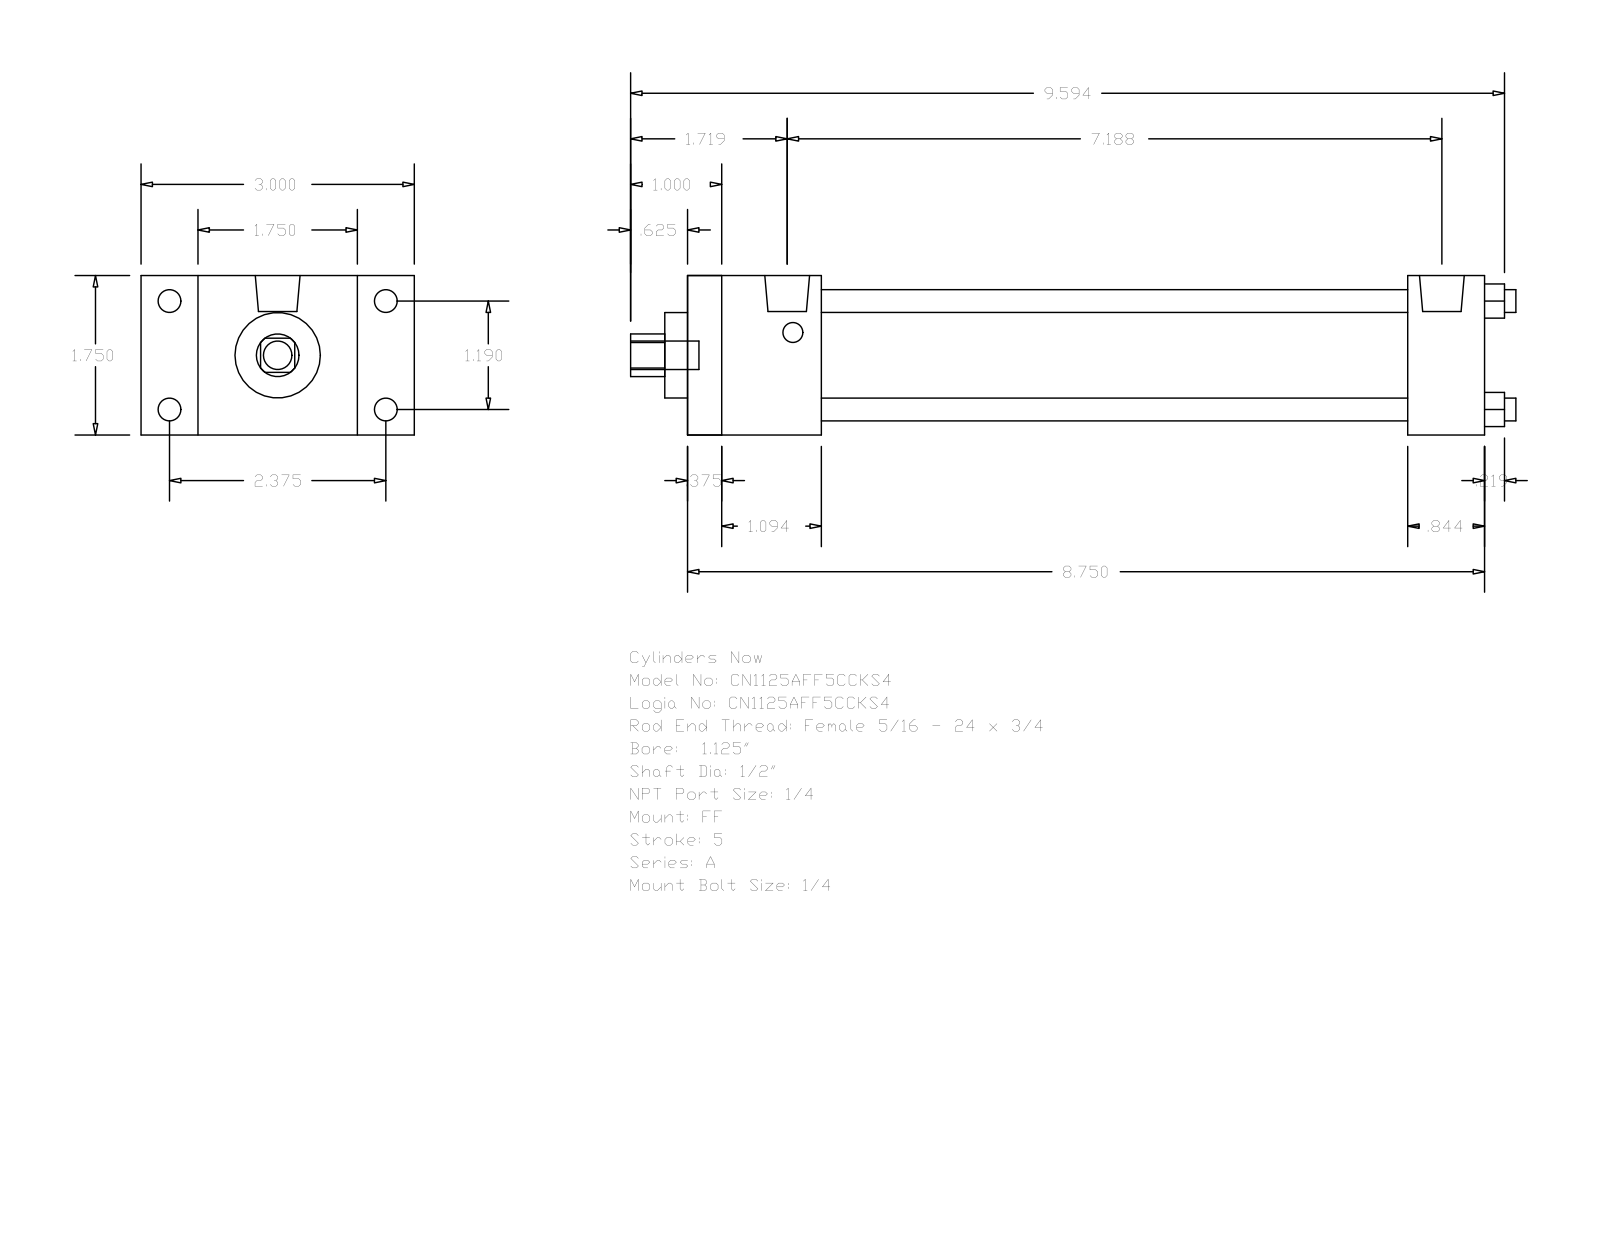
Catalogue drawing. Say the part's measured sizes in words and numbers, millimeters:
The part is named "A_FF__0112_0.5". Its 3-D file was written by "GSSL Pune (CONFIG_CONTROL_DESIGN)". It is 0 solids with 92 faces: 64 planar, 28 cylindrical and 0 other. Overall it measures 246.86 by 76.2 by 44.45 millimeters. Round holes: 4 of diameter 6.35, 1 of diameter 12.7, 1 of diameter 23.81, 1 of diameter 31.88. Round bosses or shafts: 4 of diameter 6.35, 4 of diameter 5.56, 2 of diameter 12.49, 1 of diameter 7.94. Partial cylindrical surfaces (rounded edges, fillets, slot ends): 1 of radius 5.94. The main face-to-face distances are 44.46, 222.24, 9.52, 212.72, 15.87, 200.81, 191.29, 21.43, 37.3, 27.78. The hole center spacings are 21.37, 30.22, 42.74.
